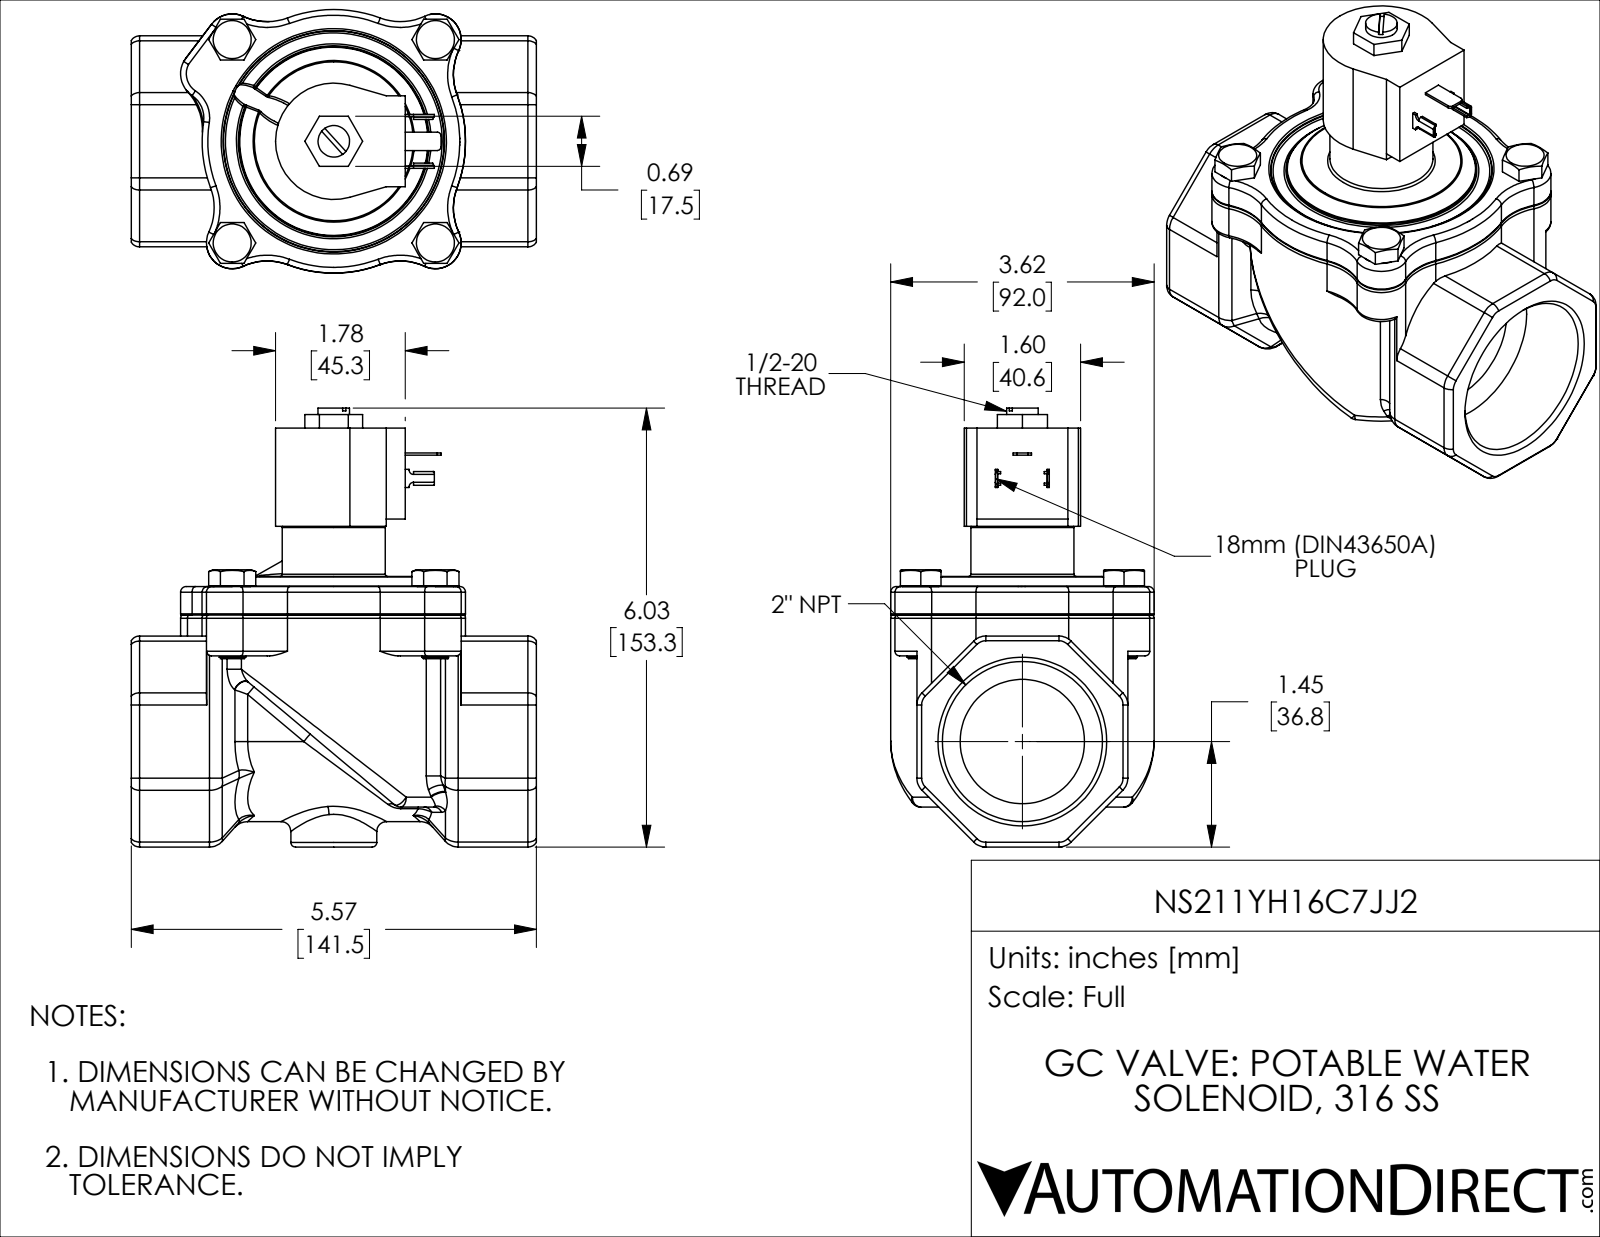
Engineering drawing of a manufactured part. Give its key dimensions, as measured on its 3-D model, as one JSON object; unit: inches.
{"part_name": "NS211YH16C7JJ2", "step_written_by": "SolidWorks 2024 (CONFIG_CONTROL_DESIGN)", "units": "inches", "bodies": {"solids": 9, "faces": 606, "planar": 166, "cylindrical": 205, "other": 235}, "overall_size": [6.034, 5.571, 3.622], "volume_in3": 37.3, "surface_area_in2": 171.8, "round_holes": [[0.31, 4], [0.433, 4], [0.12, 1], [0.125, 1], [0.236, 1], [0.434, 1], [0.504, 1], [0.846, 1], [0.949, 1], [1.71, 1], [2.2, 1], [2.874, 1]], "round_bosses_or_shafts": [[0.504, 4], [0.37, 4], [3.024, 1], [1.417, 1], [1.181, 1]], "partial_cylinders_radius": [[0.136, 29], [0.236, 28], [0.787, 15], [0.354, 8], [0.006, 4], [0.041, 4], [0.05, 2], [0.06, 2]], "face_to_face_distances": [0.118, 2.207, 3.364, 2.9, 2.9, 0.511, 0.393, 1.35, 1.338, 1.22], "hole_center_spacings": [1.976, 1.976, 2.795, 2.795, 1.976, 2.351, 2.794, 2.796]}
